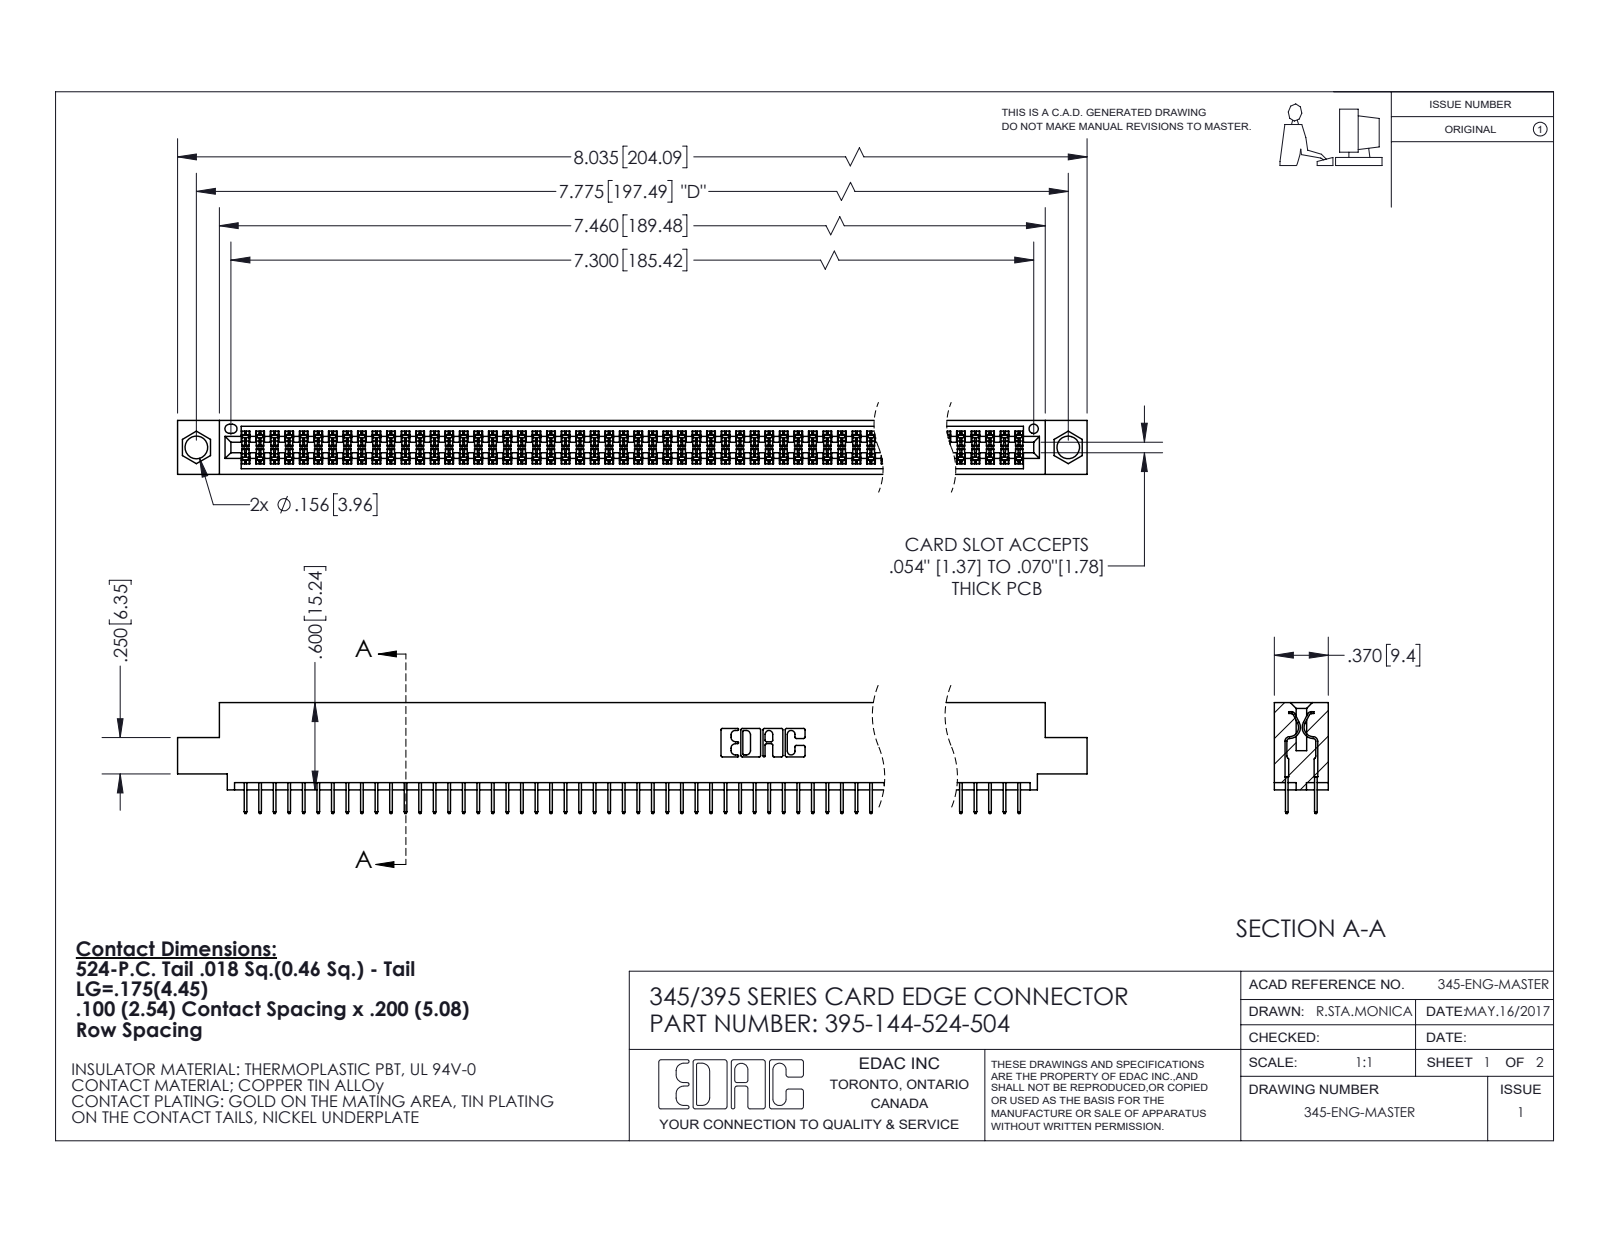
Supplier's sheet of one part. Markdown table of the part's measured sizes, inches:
| quantity | value |
| --- | --- |
| part name | 345 Part_0.110 Offset - 0.156 Dia-TI; 345-292-001_345-293-124; 395-144-524-504 |
| STEP written by | SolidWorks 2020 (CONFIG_CONTROL_DESIGN) |
| units | inches |
| bodies | 145 solids, 7920 faces (5714 planar, 2206 cylindrical, 0 other) |
| overall size | 8.035 × 0.762 × 0.37 |
| volume | 1.203 in³ |
| surface area | 45.07 in² |
| round holes (diameter × count) | 0.156 × 2, 0.064 × 1 |
| partial cylindrical surfaces (radius × count) | 0.006 × 216, 0.01 × 22, 0.007 × 6, 0.031 × 6, 0.026 × 3, 0.014 × 2, 0.019 × 2, 0.022 × 2 |
| main face-to-face distances | 0.072, 0.298, 0.2, 0.37, 0.098, 0.272, 0.025, 0.225, 0.072, 0.175 |
| hole center spacings | 0.27, 7.539, 7.775 |
